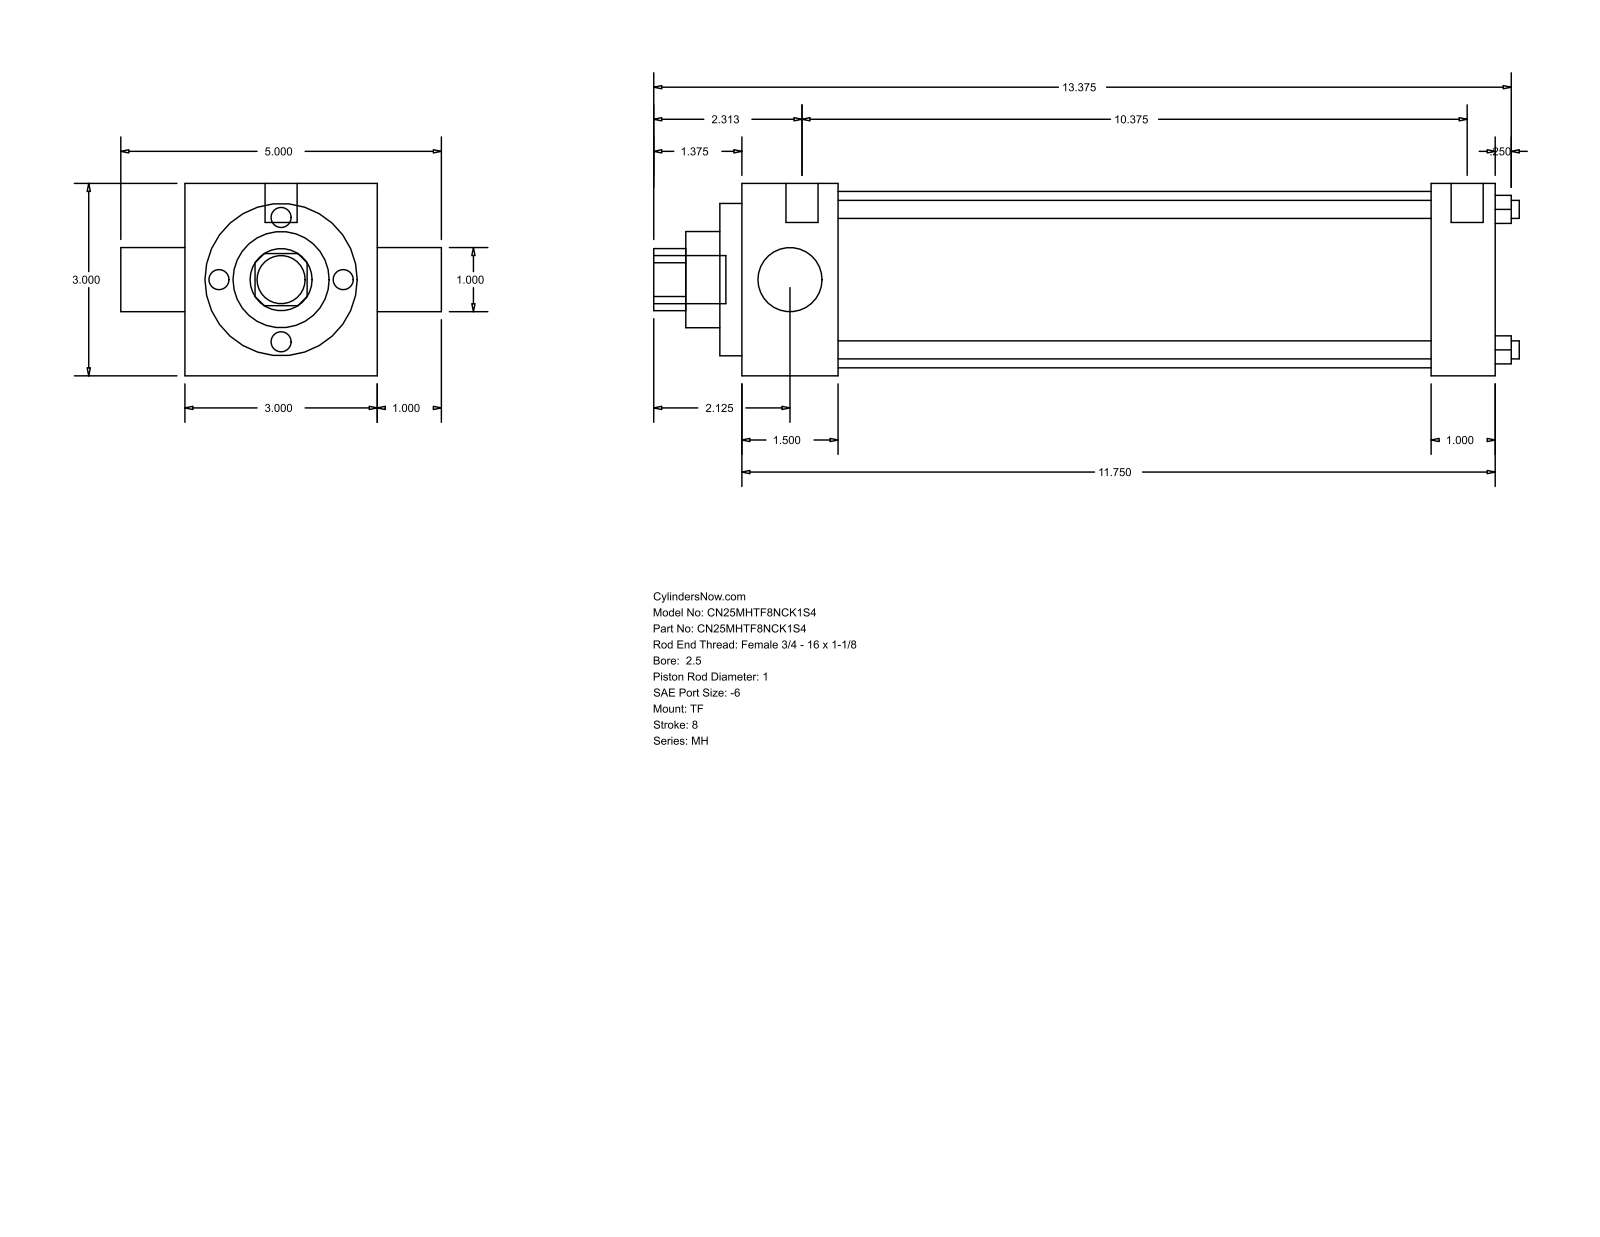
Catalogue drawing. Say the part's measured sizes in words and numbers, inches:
The part is named "MH_TF__0250_1". Its 3-D file was written by "GSSL Pune (CONFIG_CONTROL_DESIGN)". It is 0 solids with 86 faces: 61 planar, 25 cylindrical and 0 other. Overall it measures 13.5 by 5 by 3 inches. Round holes: 4 of diameter 0.281, 2 of diameter 1, 1 of diameter 1.5, 1 of diameter 2.375, 1 of diameter 2.75. Round bosses or shafts: 3 of diameter 0.219, 2 of diameter 0.5, 1 of diameter 0.75. Partial cylindrical surfaces (rounded edges, fillets, slot ends): 1 of radius 0.484. The main face-to-face distances are 3, 11.75, 1, 1.5, 10.25, 10.75, 9.25, 0.344, 1.844, 11.094. The hole center spacings are 1.548, 2.19, 3.097.
